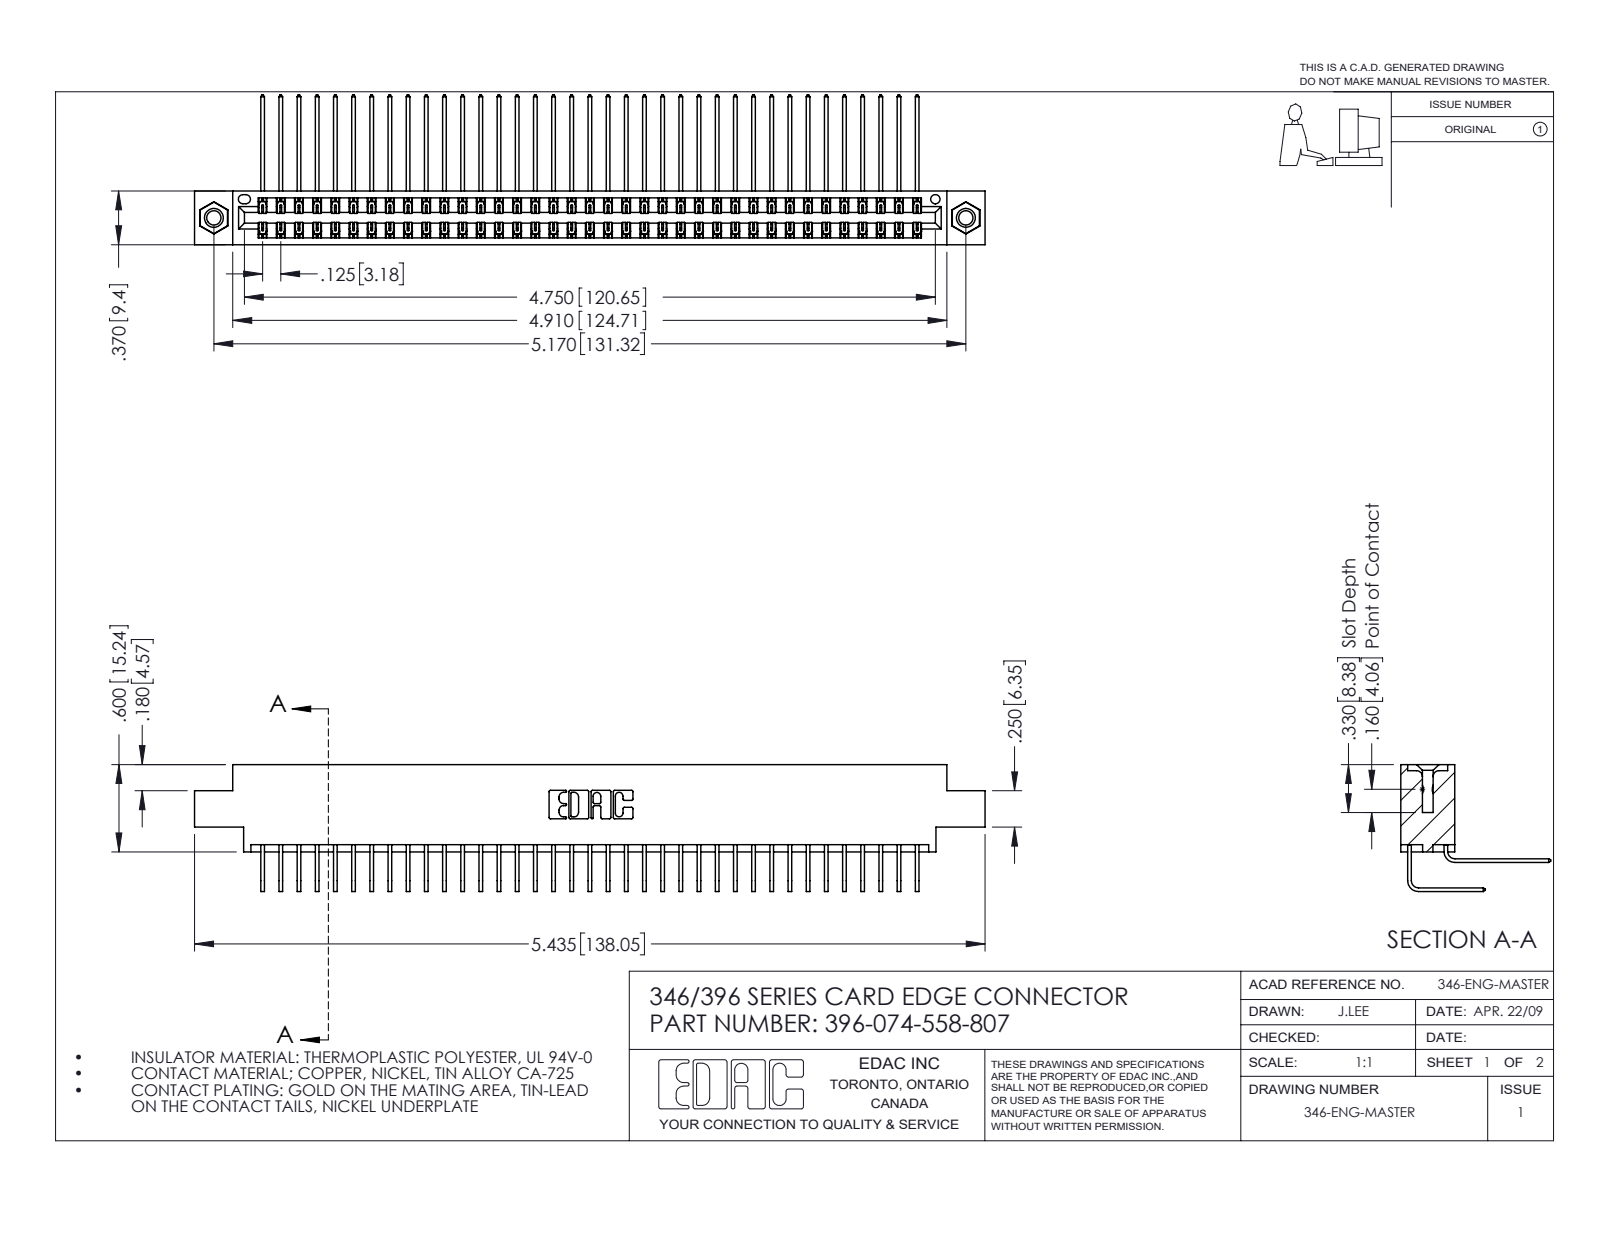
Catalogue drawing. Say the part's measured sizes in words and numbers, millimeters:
The part is named "396-074-558-807; 345-292-001_558 Tail - 2; 345-250-001_345-250-005-103; 345-292-001_558 559 Tail - 1 (+1 more)". Its 3-D file was written by "SolidWorks 2016 (CONFIG_CONTROL_DESIGN)". It is 77 solids with 4182 faces: 2850 planar, 1316 cylindrical and 16 other. Overall it measures 138 by 26.2 by 22.2 millimeters. Its volume is 13 700 cubic millimeters and its surface area 20 990 square millimeters. Round holes: 2 of diameter 2.5, 2 of diameter 3.2, 2 of diameter 4, 1 of diameter 1.6. Round bosses or shafts: 2 of diameter 3.9. Partial cylindrical surfaces (rounded edges, fillets, slot ends): 111 of radius 0.2, 22 of radius 0.3, 6 of radius 0.2, 6 of radius 0.8, 3 of radius 0.7, 2 of radius 0.4, 2 of radius 0.6, 2 of radius 0.6. The main face-to-face distances are 8.2, 1.2, 0.6, 9.4, 6.4, 7.6, 1.8, 7, 5.6, 3.8. The hole center spacings are 6.2, 126, 131.3.
